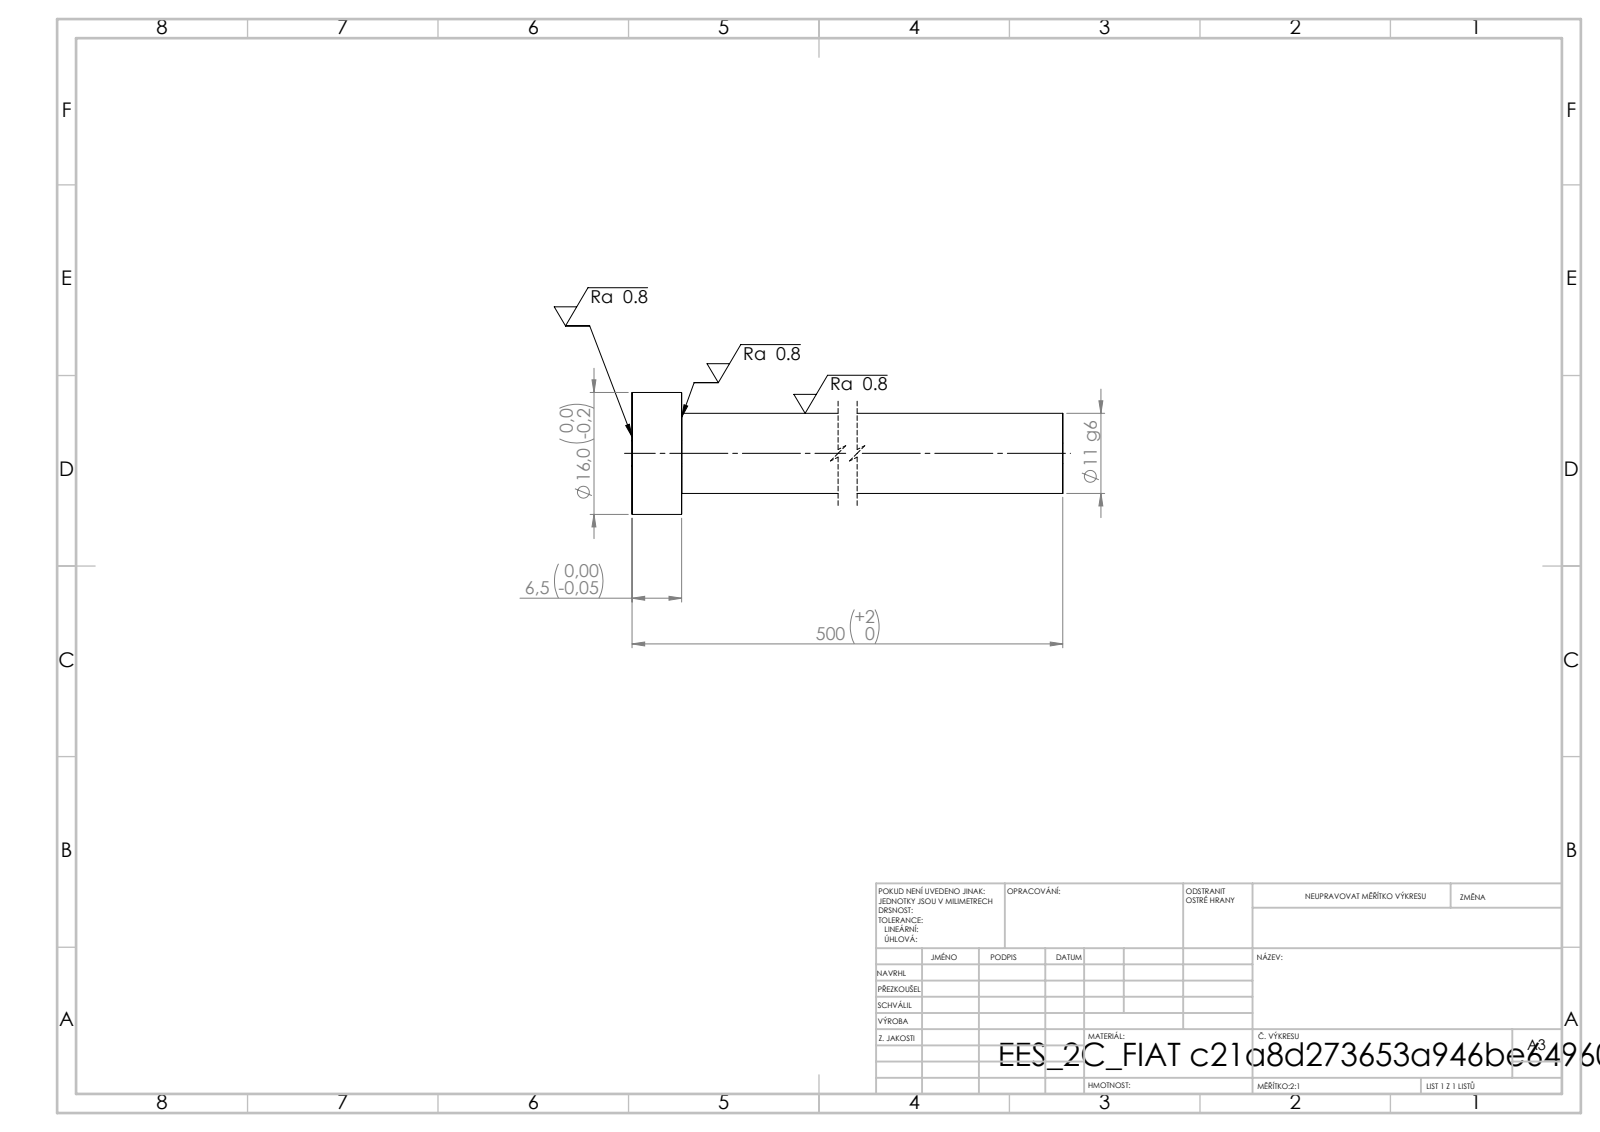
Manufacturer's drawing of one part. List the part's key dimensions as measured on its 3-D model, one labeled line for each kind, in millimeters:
STEP written by: SolidWorks 2019 (CONFIG_CONTROL_DESIGN)
Units: millimetres
Bodies: 1 solid, 7 faces (3 planar, 4 cylindrical, 0 other)
Overall size (bounding box): 500 × 16 × 16
Volume: 44 039 mm³ · Surface area: 17 008 mm²
Round bosses / shafts (diameter × count): ⌀16 ×1, ⌀10.5 ×1
Main face-to-face distances: 6.5, 500, 493.5
